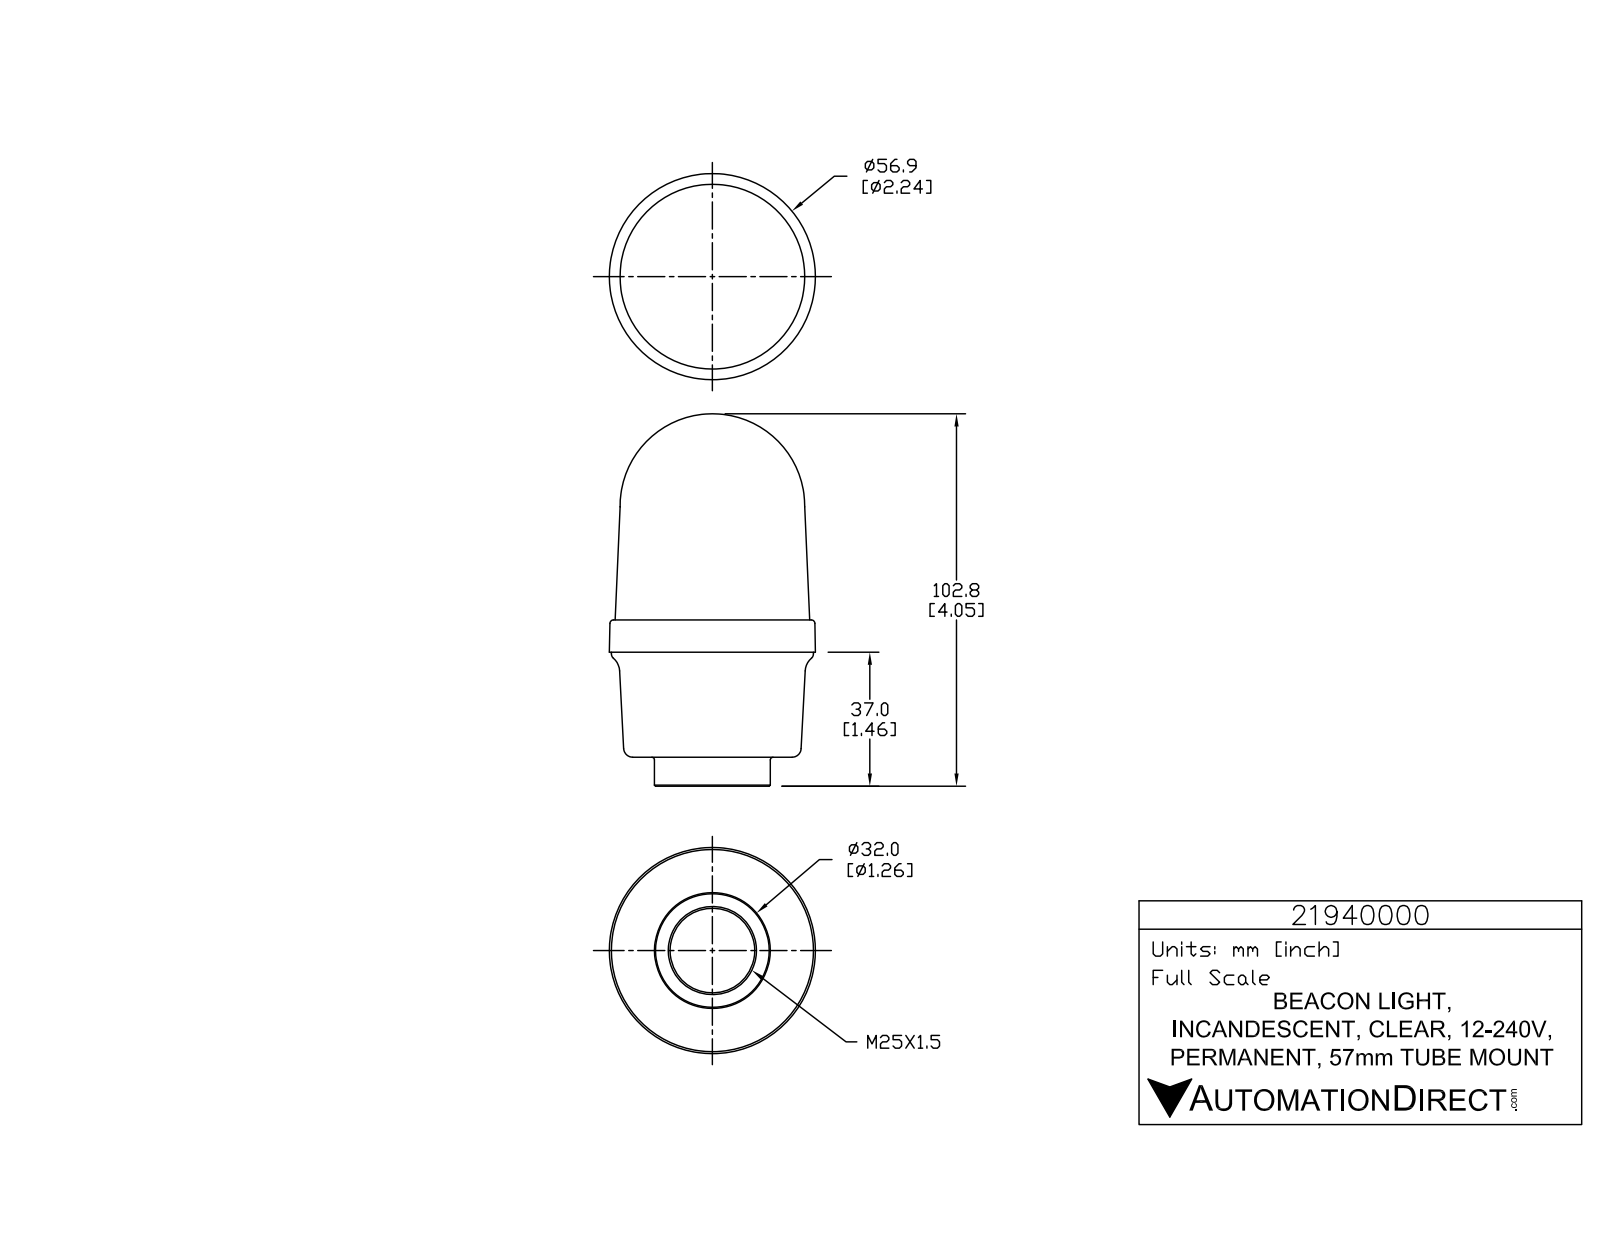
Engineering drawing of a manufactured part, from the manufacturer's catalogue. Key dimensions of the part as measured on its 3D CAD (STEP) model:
Part name (STEP PRODUCT): 21940000
STEP written by: SolidWorks 2015 (AUTOMOTIVE_DESIGN)
Units: millimetres
Bodies: 1 solid, 764 faces (524 planar, 145 cylindrical, 95 other)
Overall size (bounding box): 102.8 × 56.9 × 56.9
Volume: 186 111 mm³ · Surface area: 18 965 mm²
Round holes (diameter × count): ⌀0.99 ×3, ⌀23.38 ×1
Round bosses / shafts (diameter × count): ⌀5.74 ×3, ⌀1.43 ×3, ⌀55.8 ×1, ⌀32 ×1
Partial cylindrical surfaces — rounded edges, fillets, slot ends (radius × count): R0.2 ×6, R0.21 ×6, R0.21 ×6, R3.32 ×6, R0.1 ×3, R0.12 ×3, R0.19 ×3, R0.2 ×3
Main face-to-face distances: 8, 29, 37, 8.9, 37.9, 45.9, 10.61, 19.51, 48.51, 56.51
